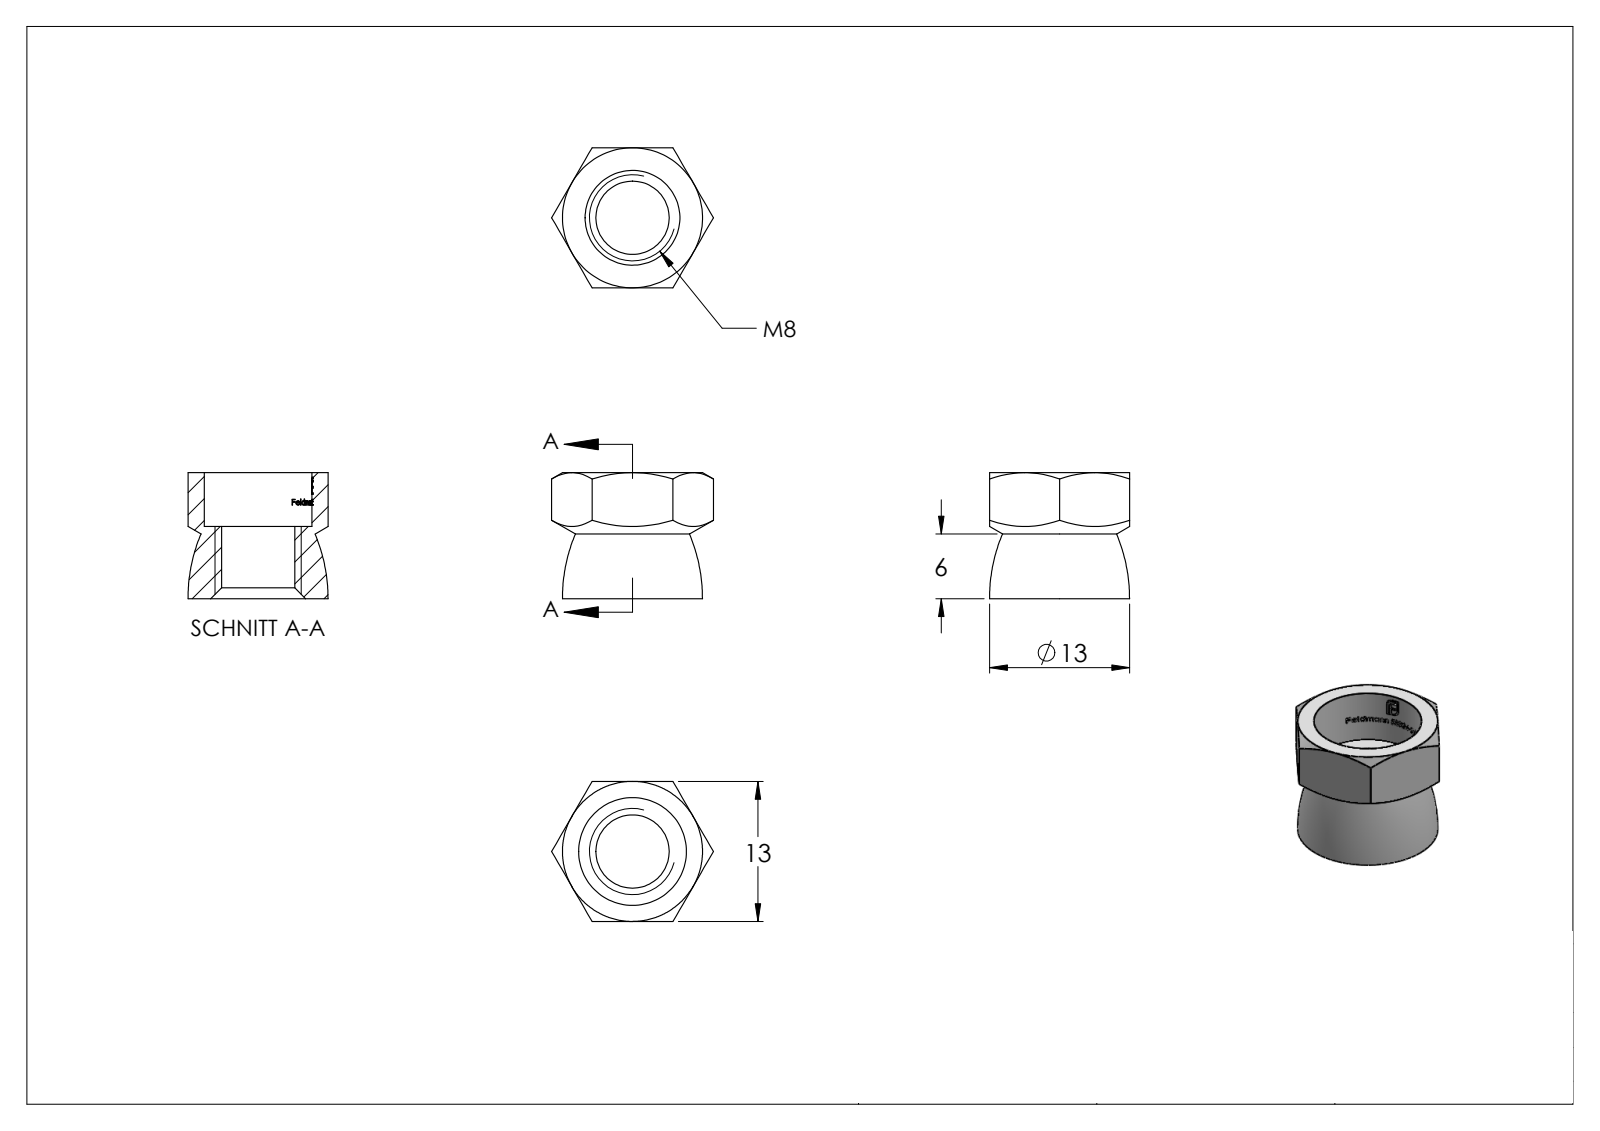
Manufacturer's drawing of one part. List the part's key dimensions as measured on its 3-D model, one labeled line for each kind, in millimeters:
Part name (STEP PRODUCT): 58324-240-8
STEP written by: SolidWorks 2018 (CONFIG_CONTROL_DESIGN)
Units: millimetres
Bodies: 1 solid, 320 faces (143 planar, 31 cylindrical, 146 other)
Overall size (bounding box): 15.01 × 13 × 11.69
Volume: 861 mm³ · Surface area: 1 014 mm²
Round holes (diameter × count): ⌀6.8 ×1, ⌀10 ×1
Partial cylindrical surfaces — rounded edges, fillets, slot ends (radius × count): R5.1 ×1
Main face-to-face distances: 13, 11.69, 6.69, 5, 0.87, 0.81, 2.45, 1.1, 0.47, 4.29
